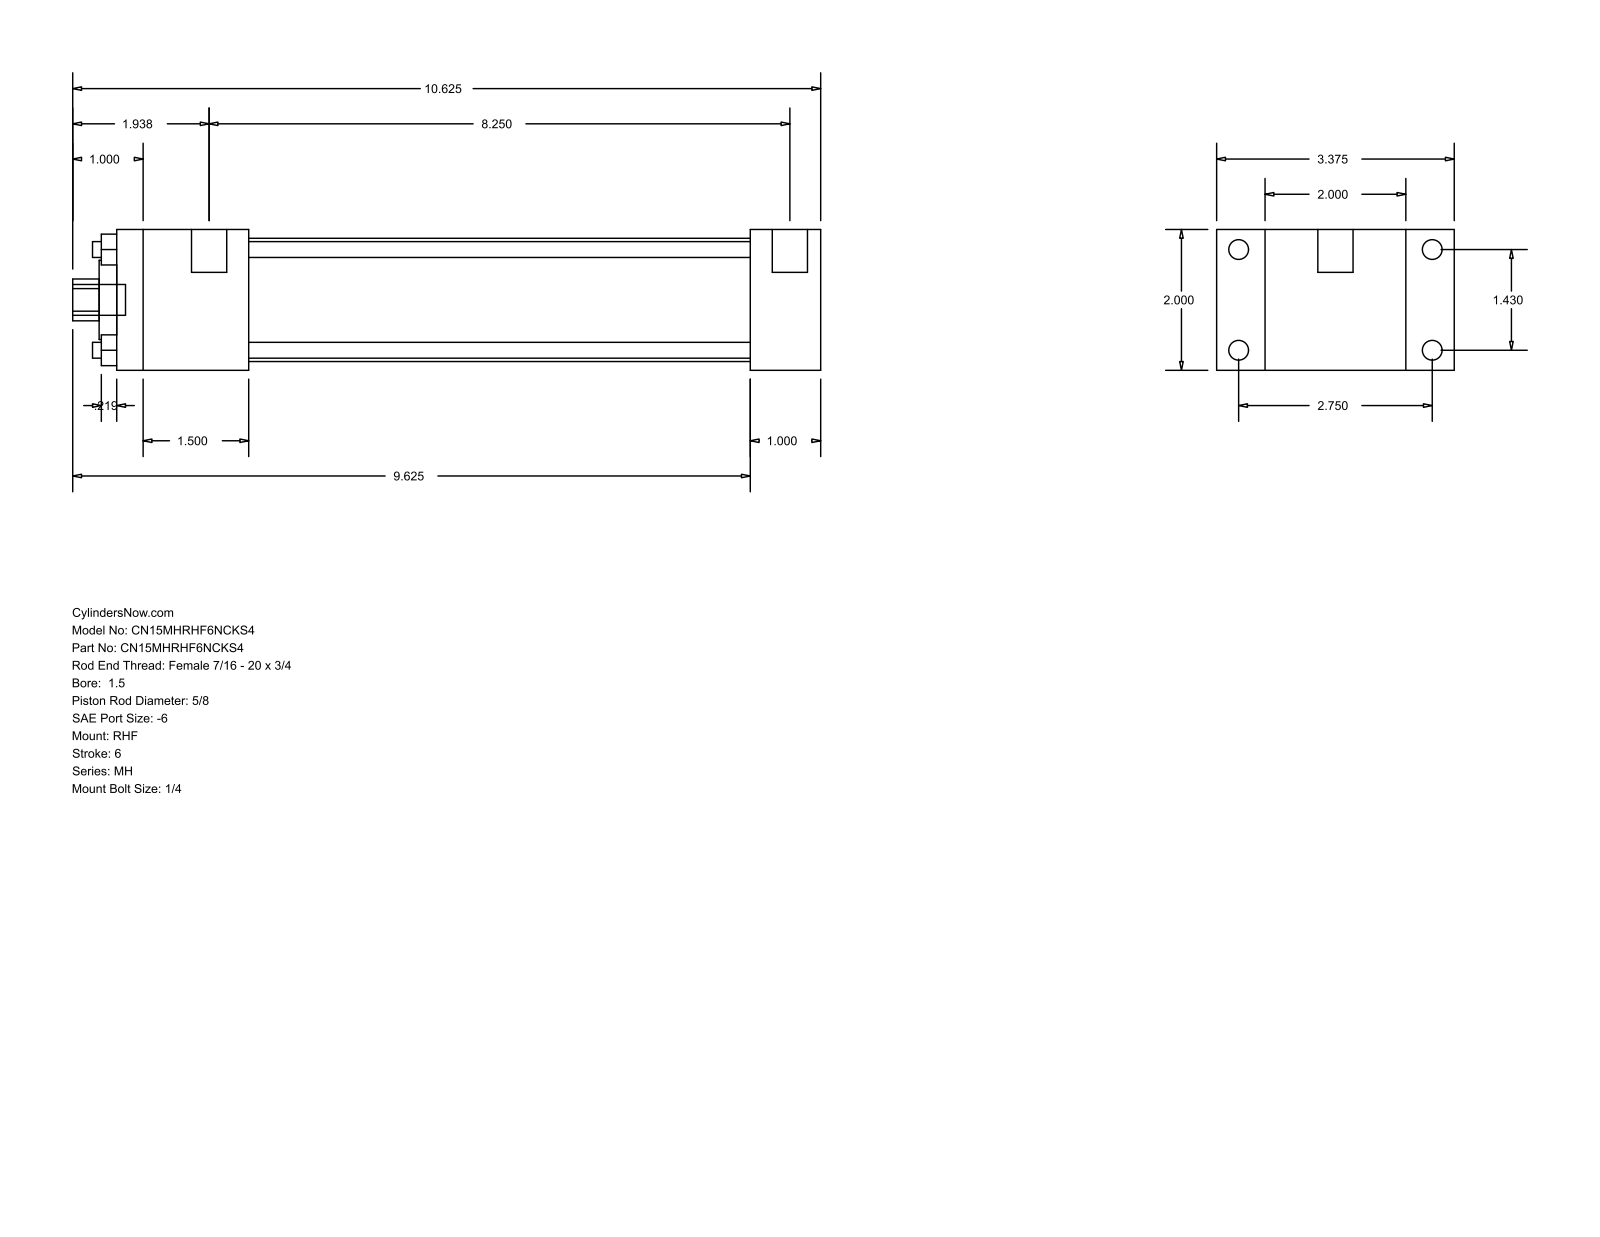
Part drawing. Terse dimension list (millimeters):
name: MH_RHF__0150_0.625
written by: GSSL Pune (CONFIG_CONTROL_DESIGN)
unit: mm
bodies: 0 solids, 88 faces (60 planar, 28 cylindrical, 0 other)
size: 269.88 × 85.72 × 50.8
holes: 4× ⌀5.71, 1× ⌀15.88, 1× ⌀28.57, 1× ⌀44.45
bosses: 4× ⌀7.14, 4× ⌀5.56, 2× ⌀12.7, 1× ⌀11.11
rounds: 1× R7.54
face distances: 50.8, 17.46, 68.26, 25.41, 228.59, 254, 85.72, 47.62, 180.97, 206.38
hole spacings: 25.68, 36.32, 51.36
